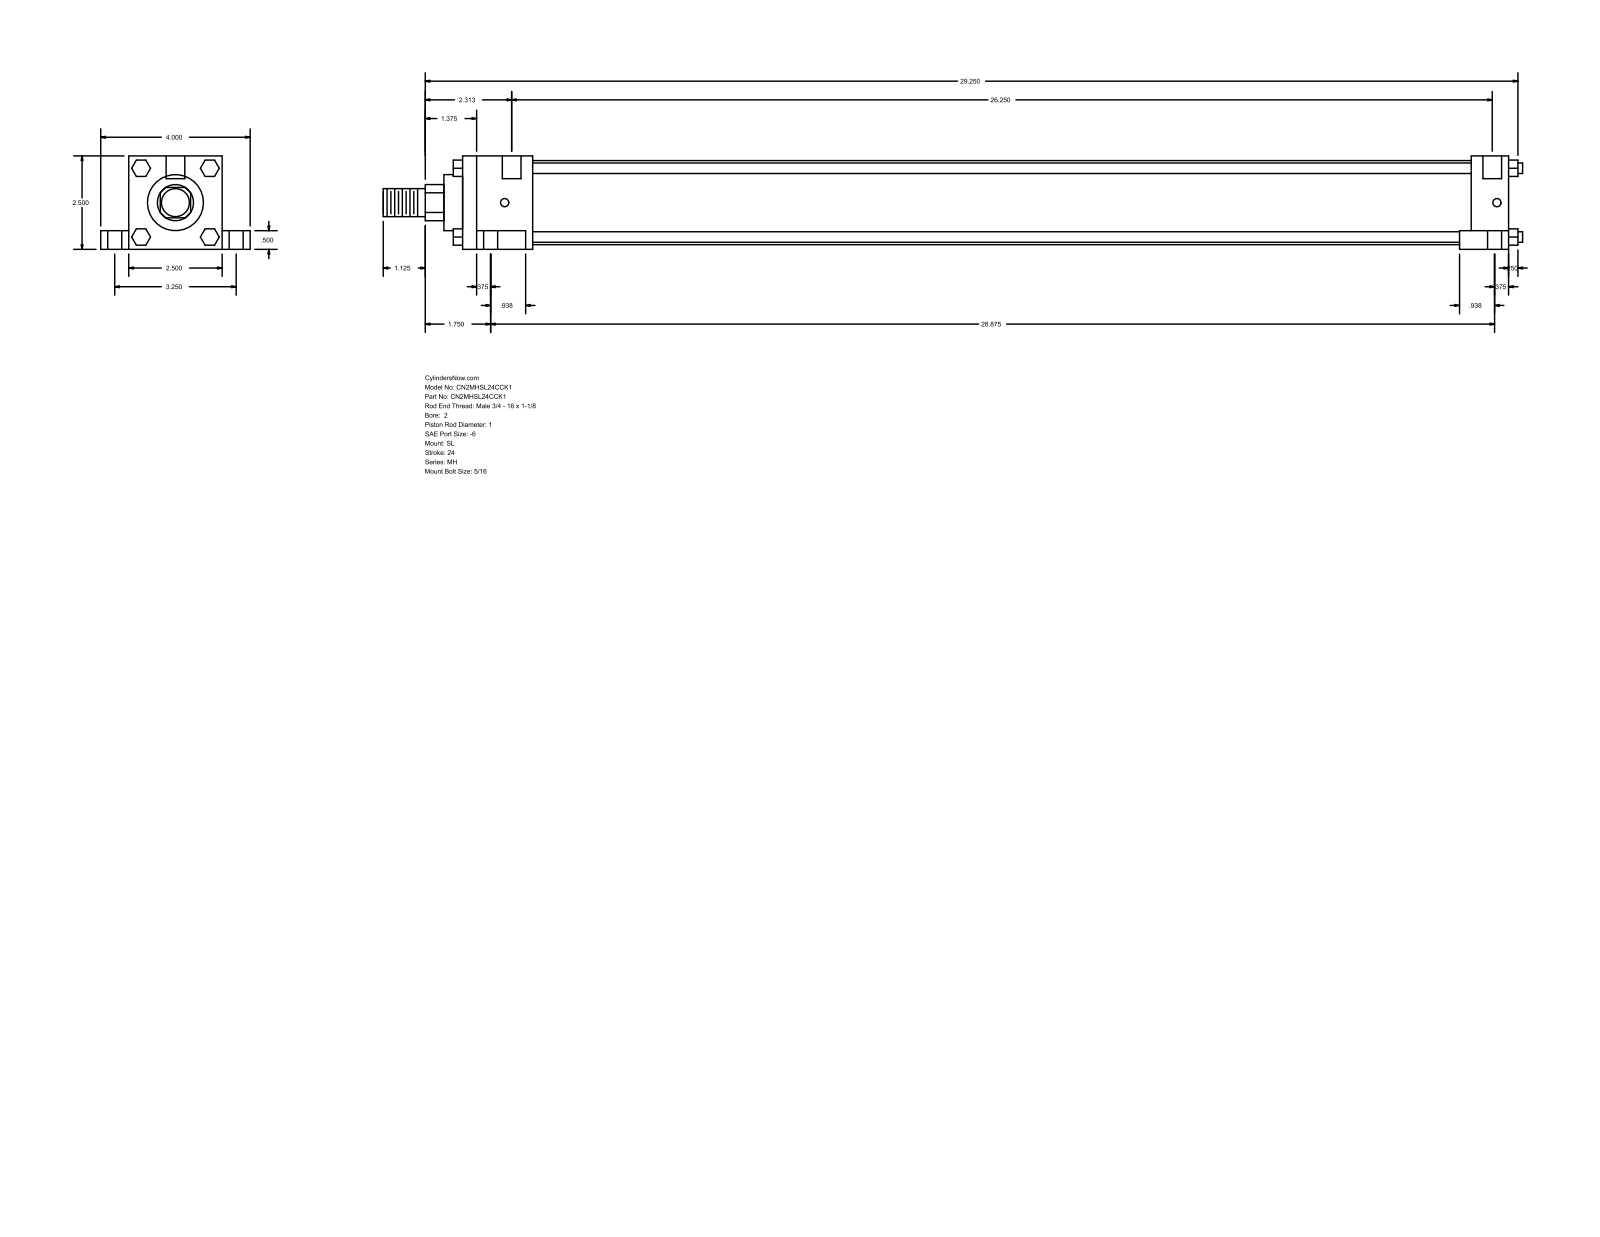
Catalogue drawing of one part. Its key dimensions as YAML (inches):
part_name: "MH_SL__0200_1"
step_written_by: "GSSL Pune (CONFIG_CONTROL_DESIGN)"
units: inches
bodies: {solids: 0, faces: 148, planar: 112, cylindrical: 36, other: 0}
overall_size: [30.5, 4, 2.5]
round_holes:
  - {diameter: 0.219, count: 4}
  - {diameter: 0.375, count: 4}
  - {diameter: 0.625, count: 4}
  - {diameter: 0.5, count: 2}
round_bosses_or_shafts:
  - {diameter: 0.281, count: 4}
  - {diameter: 2.25, count: 1}
  - {diameter: 1.5, count: 1}
  - {diameter: 1, count: 1}
  - {diameter: 0.75, count: 1}
partial_cylinders:
  - {radius: 0.484, count: 1}
face_to_face_distances: [2.5, 28, 0.5, 0.75, 2, 3.25, 1, 27, 1.875, 25.125]
hole_center_spacings: [1.626, 1.668, 1.719, 3.25, 26.363, 26.55, 26.562, 26.862]
